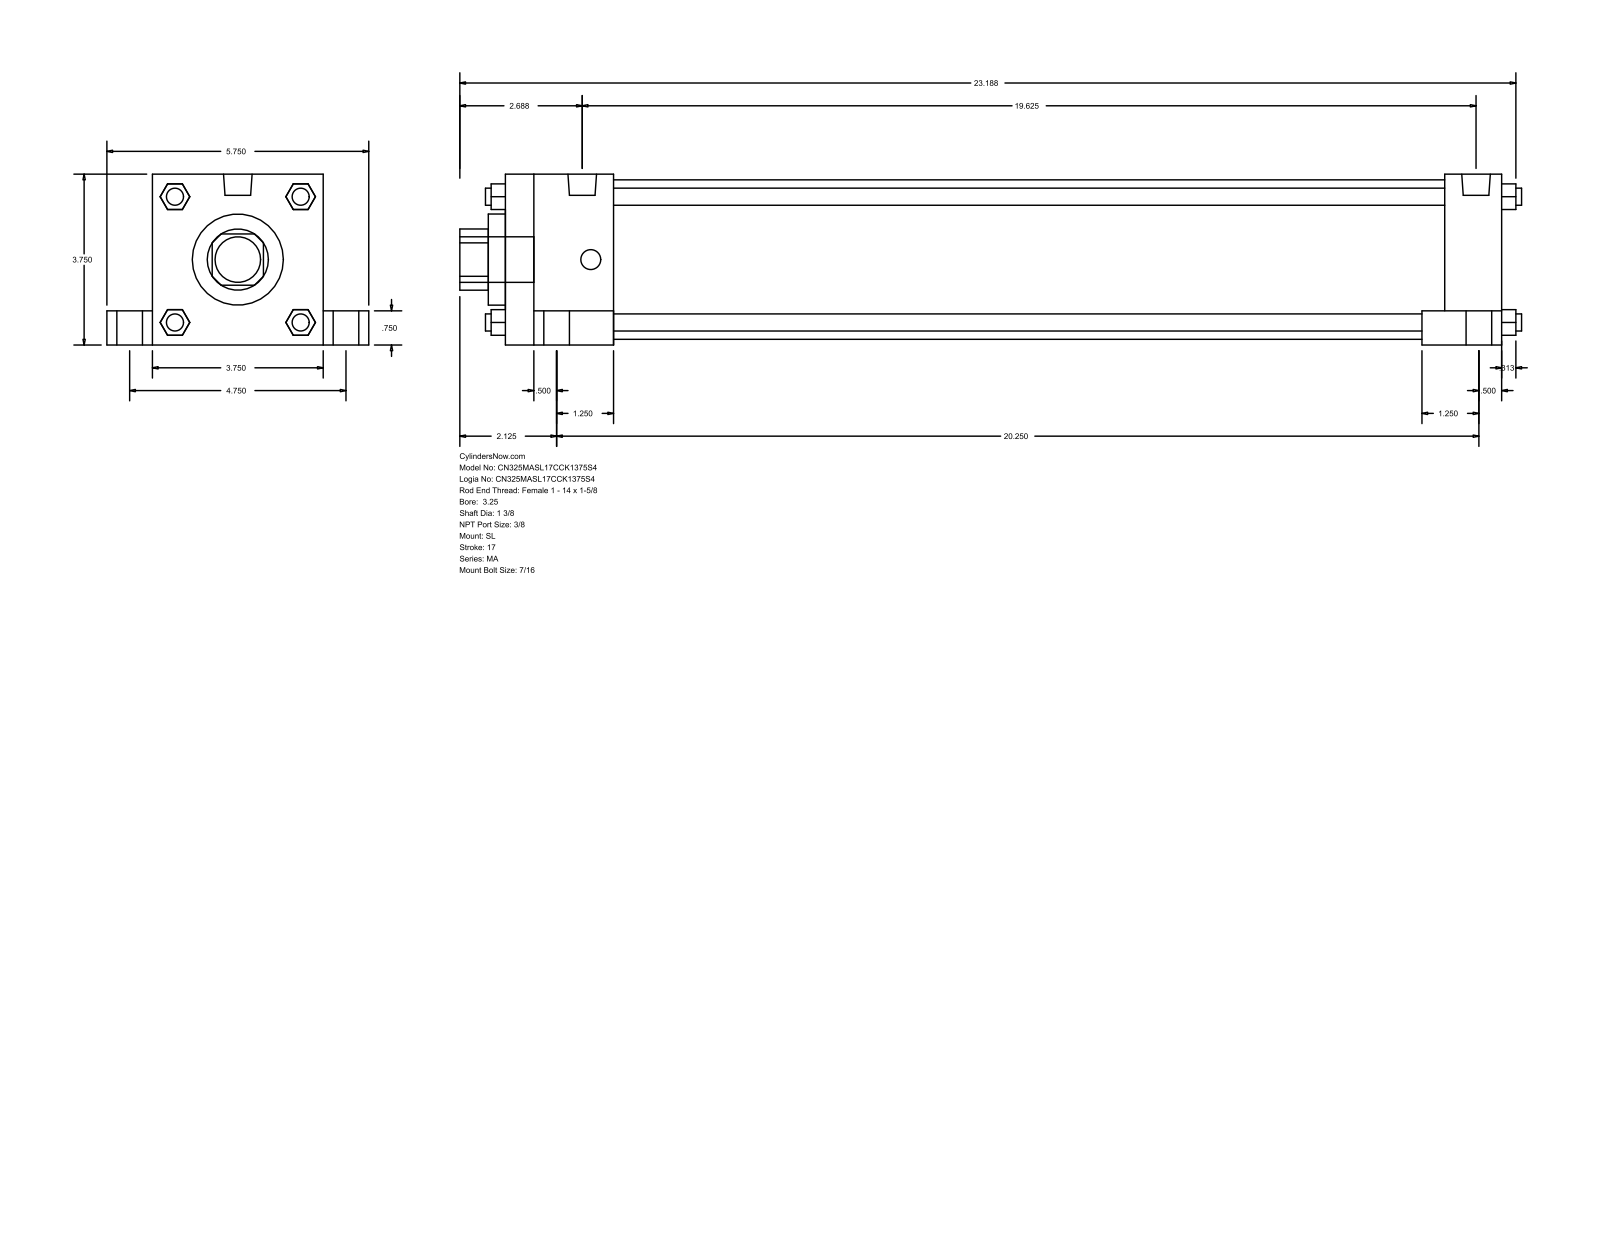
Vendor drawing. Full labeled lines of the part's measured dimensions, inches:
Part name (STEP PRODUCT): MA_SL__0325_1.375
STEP written by: GSSL Pune (CONFIG_CONTROL_DESIGN)
Units: inches
Bodies: 0 solids, 148 faces (112 planar, 36 cylindrical, 0 other)
Overall size (bounding box): 23.313 × 5.75 × 3.75
Round holes (diameter × count): ⌀1.375 ×1, ⌀2 ×1, ⌀3.5 ×1
Round bosses / shafts (diameter × count): ⌀0.813 ×4, ⌀0.563 ×4, ⌀0.437 ×4, ⌀0.375 ×4, ⌀0.627 ×2, ⌀1 ×1
Partial cylindrical surfaces — rounded edges, fillets, slot ends (radius × count): R0.672 ×1
Main face-to-face distances: 3.75, 21.875, 18.25, 1, 4.75, 20.625, 1.25, 2.375, 19.5, 0.75
